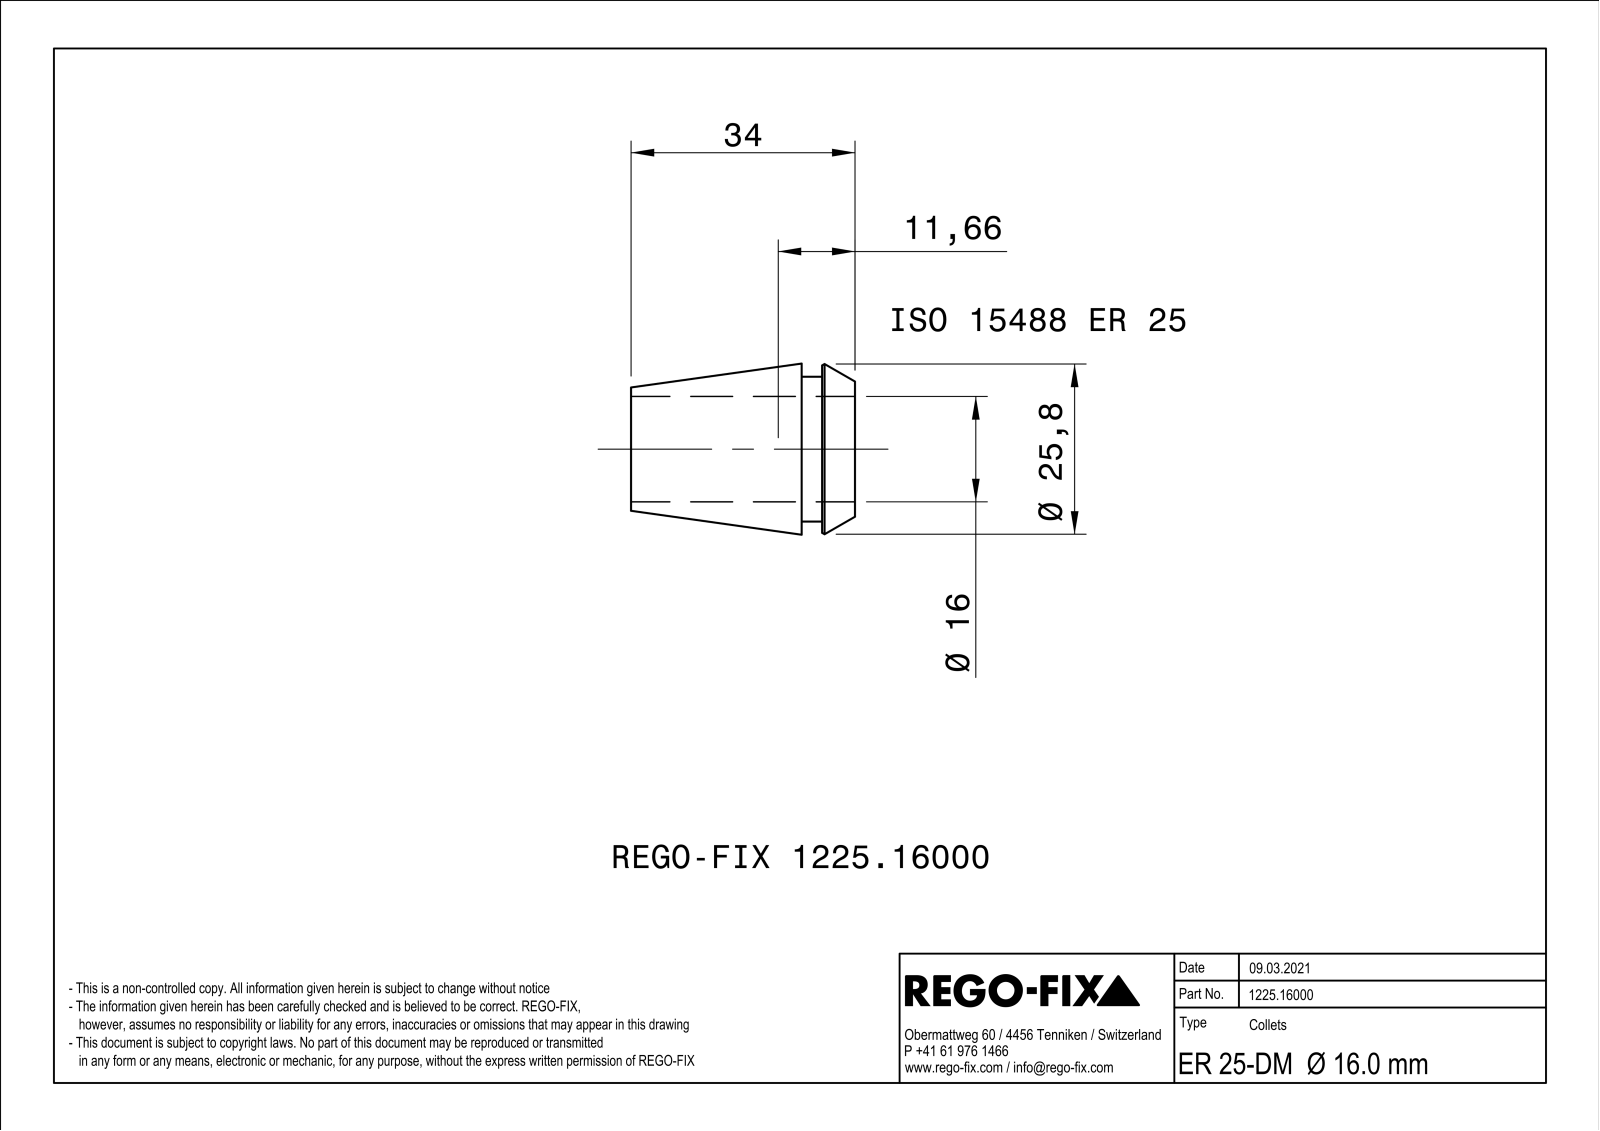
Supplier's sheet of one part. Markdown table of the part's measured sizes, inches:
| quantity | value |
| --- | --- |
| part name | NOCUT |
| STEP written by | SIEMENS PLM Software Solid Edge ST10 (AUTOMOTIVE_DESIGN) |
| units | inches |
| bodies | 1 solid, 154 faces (80 planar, 9 cylindrical, 65 other) |
| overall size | 1.339 × 1.023 × 1.023 |
| volume | 0.353 in³ |
| surface area | 10.01 in² |
| round holes (diameter × count) | 0.63 × 1 |
| round bosses / shafts (diameter × count) | 0.866 × 1 |
| main face-to-face distances | 0.031, 0.197, 0.122, 0.319, 1.142, 1.339, 1.02, 0.591, 0.394, 0.272 |
